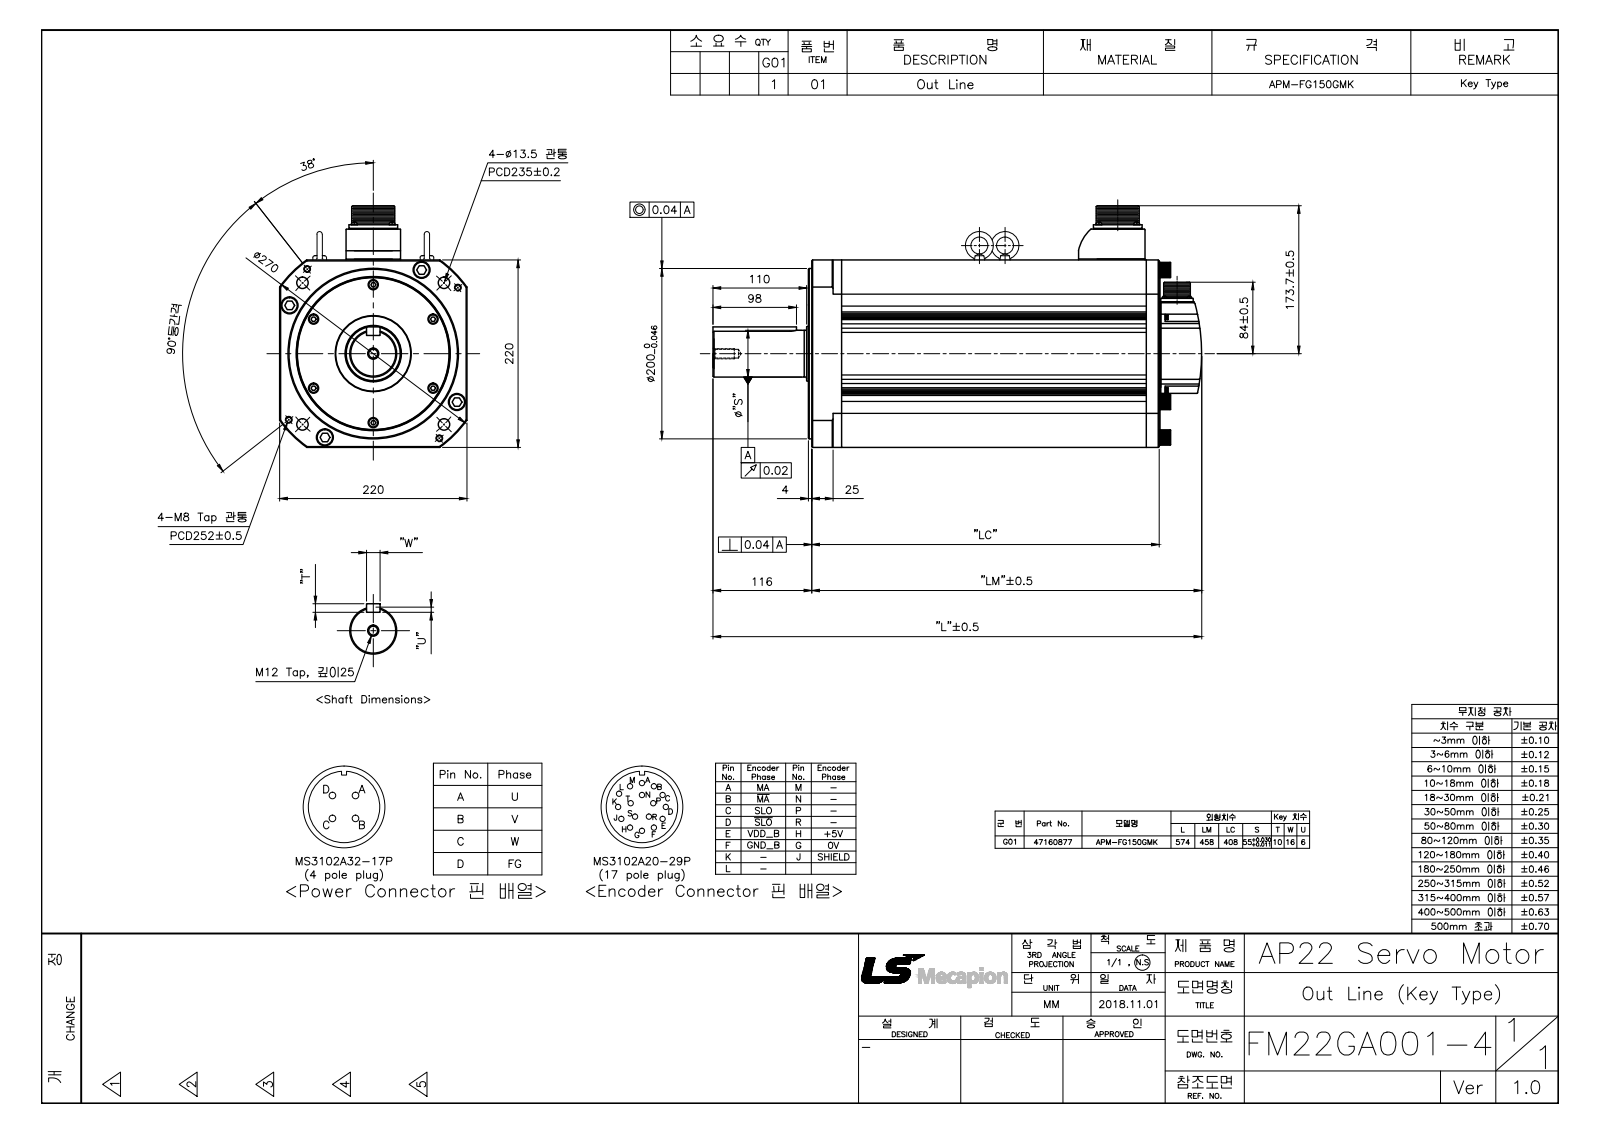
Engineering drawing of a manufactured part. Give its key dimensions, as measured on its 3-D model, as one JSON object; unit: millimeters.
{"part_name": "FM22GA001-4_Out Line(APM-FG150G_K)", "step_written_by": "SolidWorks 2011 (AUTOMOTIVE_DESIGN)", "units": "millimeters", "bodies": {"solids": 65, "faces": 2149, "planar": 746, "cylindrical": 856, "other": 547}, "overall_size": [574, 283.7, 220], "volume_mm3": 17830000, "surface_area_mm2": 1008000, "round_holes": [[12, 10], [2.5, 8], [3, 8], [6.8, 8], [13.5, 8], [20, 8], [3.05, 6], [5, 6], [6, 6], [7, 6], [8, 6], [10.2, 5]], "round_bosses_or_shafts": [[1.6, 17], [10.2, 6], [10, 6], [18, 4], [7, 4], [6, 4], [5.5, 4], [5.4, 4]], "partial_cylinders_radius": [[1, 117], [2, 17], [5, 16], [4.5, 12], [0.5, 8], [4, 4], [6, 4], [0.3, 2]], "face_to_face_distances": [358, 40, 220, 180, 17, 16, 14, 140, 397, 5], "hole_center_spacings": [81, 140.3, 17.11, 20.79, 29.4, 30.41, 31.47, 43.96]}
